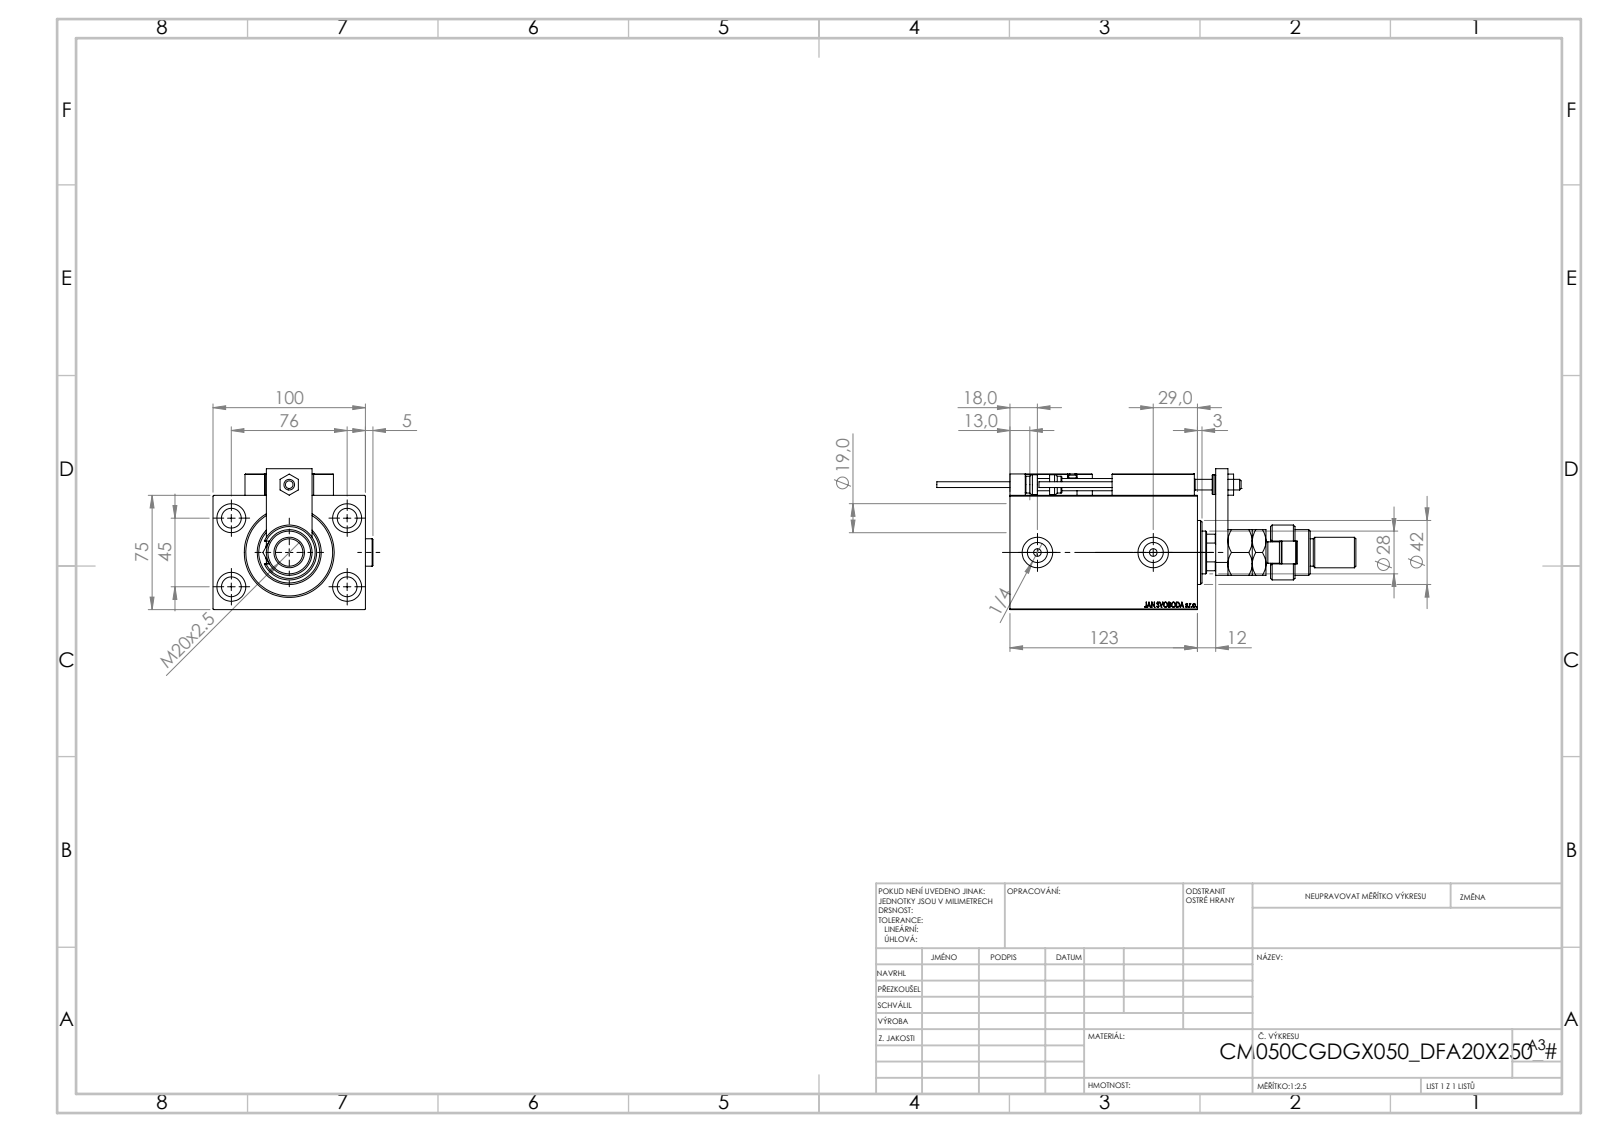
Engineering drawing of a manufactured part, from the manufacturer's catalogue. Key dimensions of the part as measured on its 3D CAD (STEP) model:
Part name (STEP PRODUCT): V450CM_VC_B; MAGNET; ALLEN BOLT D5; ZARAZKA (+8 more)
STEP written by: SolidWorks 2019 (CONFIG_CONTROL_DESIGN)
Units: millimetres
Bodies: 27 solids, 1424 faces (623 planar, 219 cylindrical, 582 other)
Overall size (bounding box): 275 × 104.9 × 92.5
Volume: 875 382 mm³ · Surface area: 168 032 mm²
Round holes (diameter × count): ⌀8 ×5, ⌀3.2 ×4, ⌀4 ×4, ⌀5 ×4, ⌀13 ×4, ⌀19 ×4, ⌀20 ×3, ⌀13.16 ×2, ⌀7 ×1, ⌀18.5 ×1, ⌀28 ×1, ⌀31.5 ×1
Round bosses / shafts (diameter × count): ⌀18 ×3, ⌀5 ×2, ⌀3.8 ×2, ⌀42 ×1, ⌀36 ×1, ⌀30 ×1, ⌀22 ×1, ⌀14 ×1
Partial cylindrical surfaces — rounded edges, fillets, slot ends (radius × count): R0.3 ×30, R3 ×2, R7.5 ×1, R12 ×1, R13.5 ×1
Main face-to-face distances: 75, 100, 14, 123, 12, 109, 20, 8, 24, 25
Hole centre spacings: 44.16, 76, 11.37, 20, 29.59, 29.69, 36.06, 42.19
